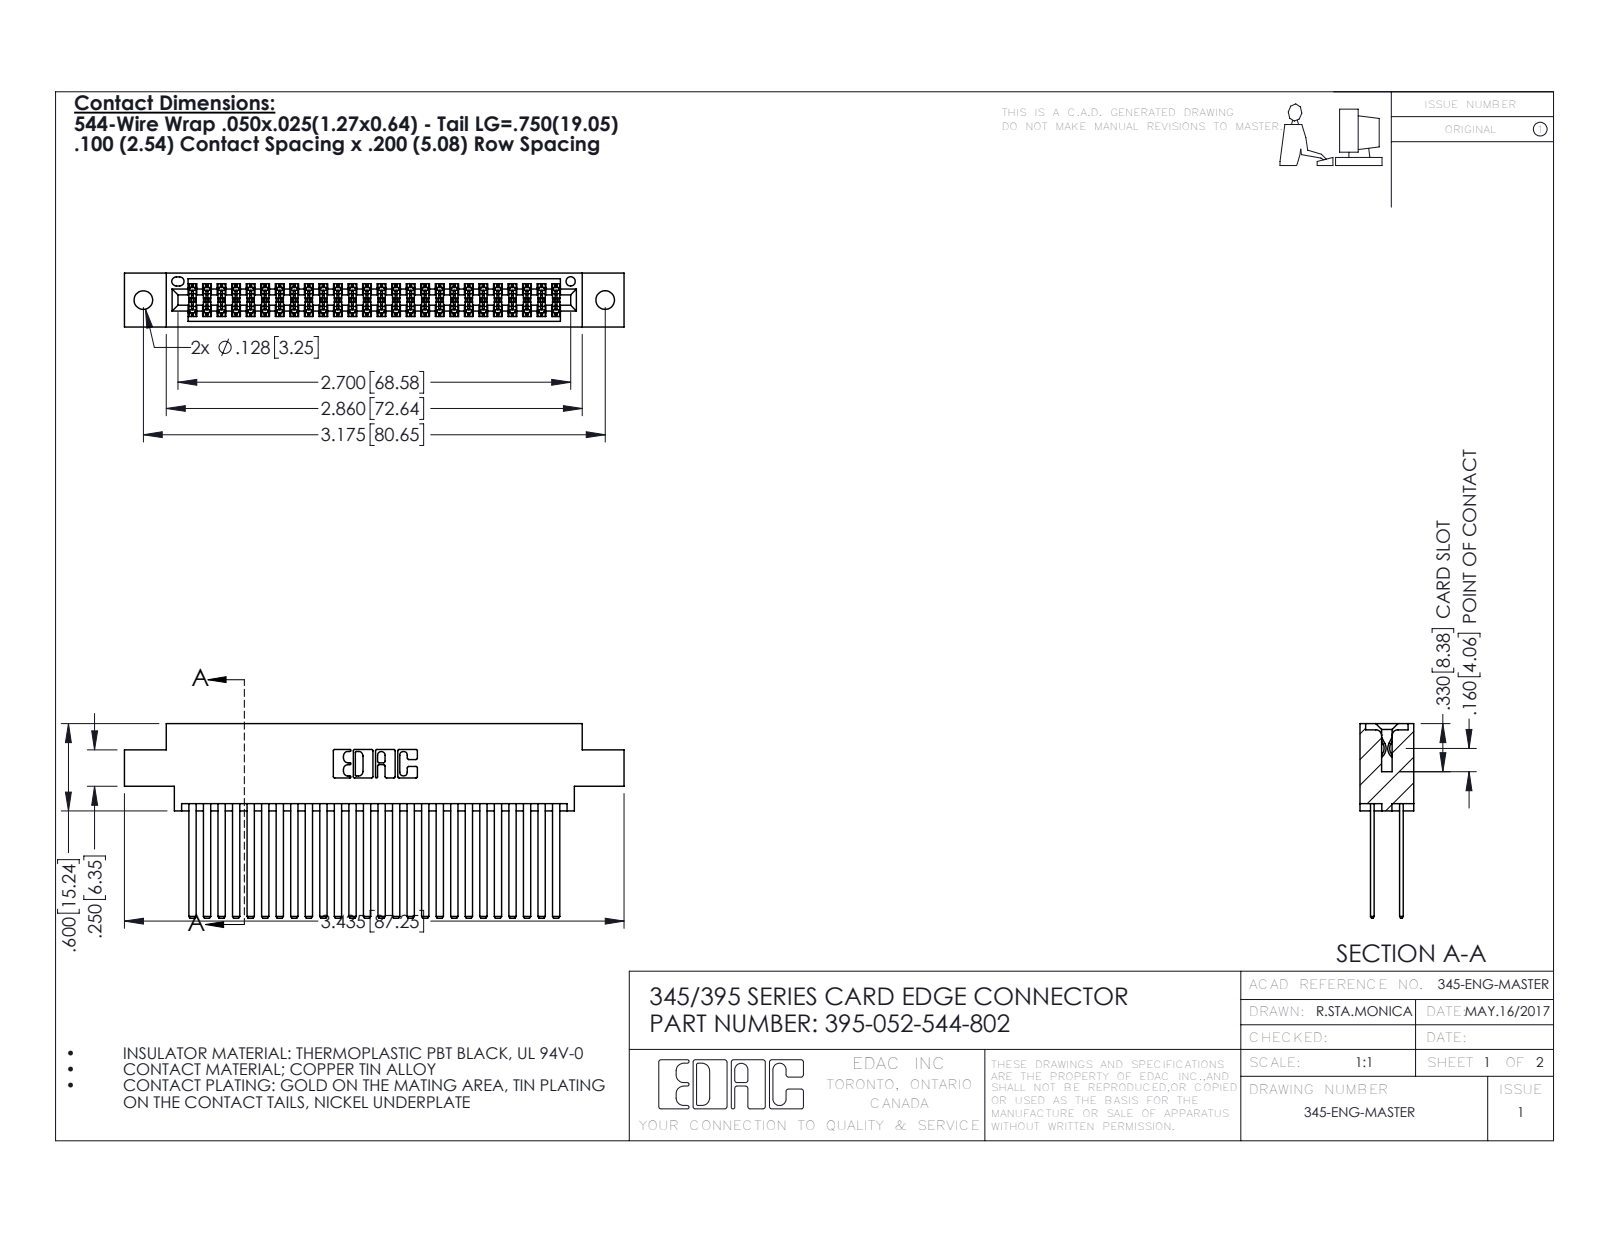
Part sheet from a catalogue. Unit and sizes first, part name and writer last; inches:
Units: inches
Overall size (bounding box): 3.435 × 1.337 × 0.37
Round holes (diameter × count): ⌀0.128 ×2, ⌀0.064 ×1
Partial cylindrical surfaces — rounded edges, fillets, slot ends (radius × count): R0.006 ×78, R0.01 ×22, R0.007 ×6, R0.031 ×6, R0.026 ×3, R0.014 ×2, R0.019 ×2, R0.022 ×2
Main face-to-face distances: 0.2, 0.025, 0.298, 0.072, 0.098, 0.272, 0.225, 0.175, 0.37, 0.15
Hole centre spacings: 0.27, 2.94, 3.175
Volume: 0.543 in³ · Surface area: 23.04 in²
Bodies: 53 solids, 2418 faces (1592 planar, 826 cylindrical, 0 other)
Part name (STEP PRODUCT): 345-292-001_345-293-144; 345 Part_0.170 Offset - 0.128 Dia; 395-052-544-802
STEP written by: SolidWorks 2016 (CONFIG_CONTROL_DESIGN)
